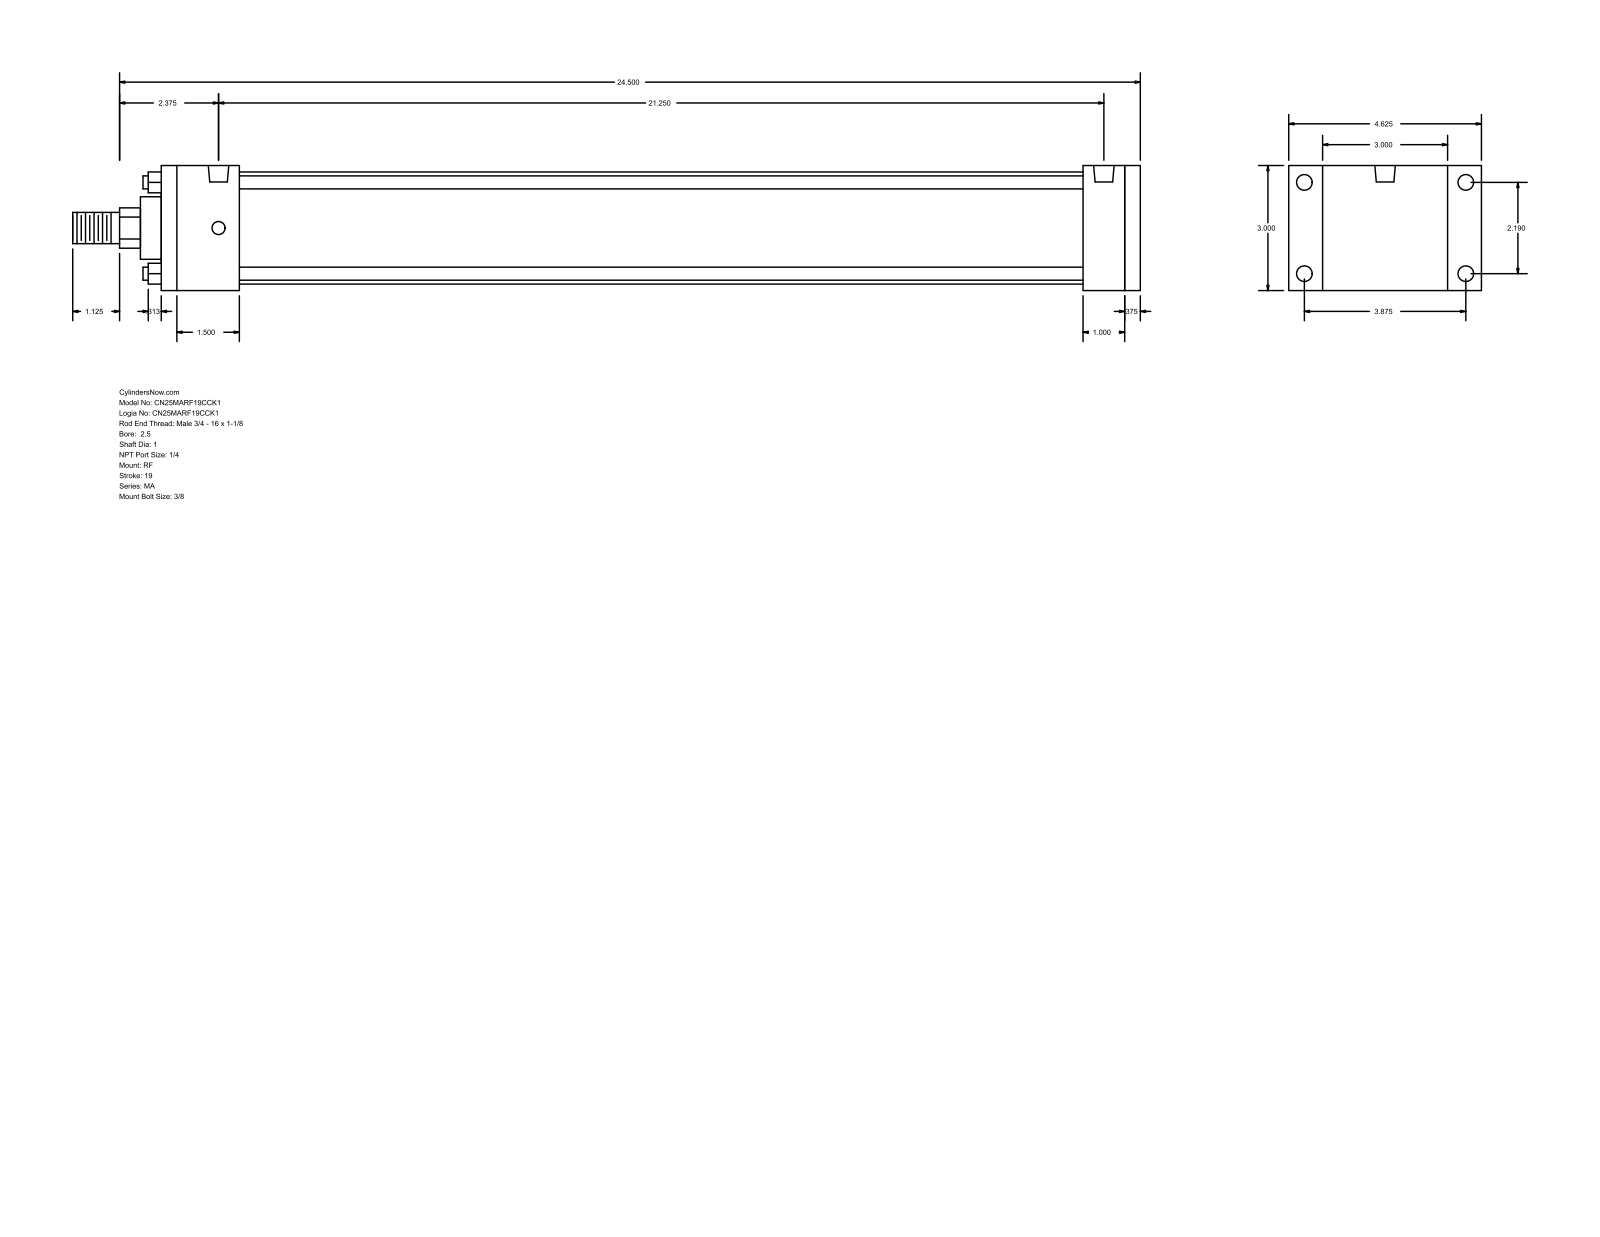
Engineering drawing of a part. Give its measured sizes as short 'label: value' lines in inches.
name: MA_RF__0250_1
written by: GSSL Pune (CONFIG_CONTROL_DESIGN)
unit: in
bodies: 0 solids, 92 faces (64 planar, 28 cylindrical, 0 other)
size: 25.625 × 4.625 × 3
holes: 4× ⌀0.313, 4× ⌀0.375, 2× ⌀0.492
bosses: 4× ⌀0.313, 1× ⌀2.69, 1× ⌀1.5, 1× ⌀1, 1× ⌀0.75
rounds: 1× R0.484
face distances: 3, 23.5, 0.375, 23.125, 1.875, 22.125, 20.25, 21.25, 21.625, 1
hole spacings: 2.19, 3.875, 4.451, 21.25
